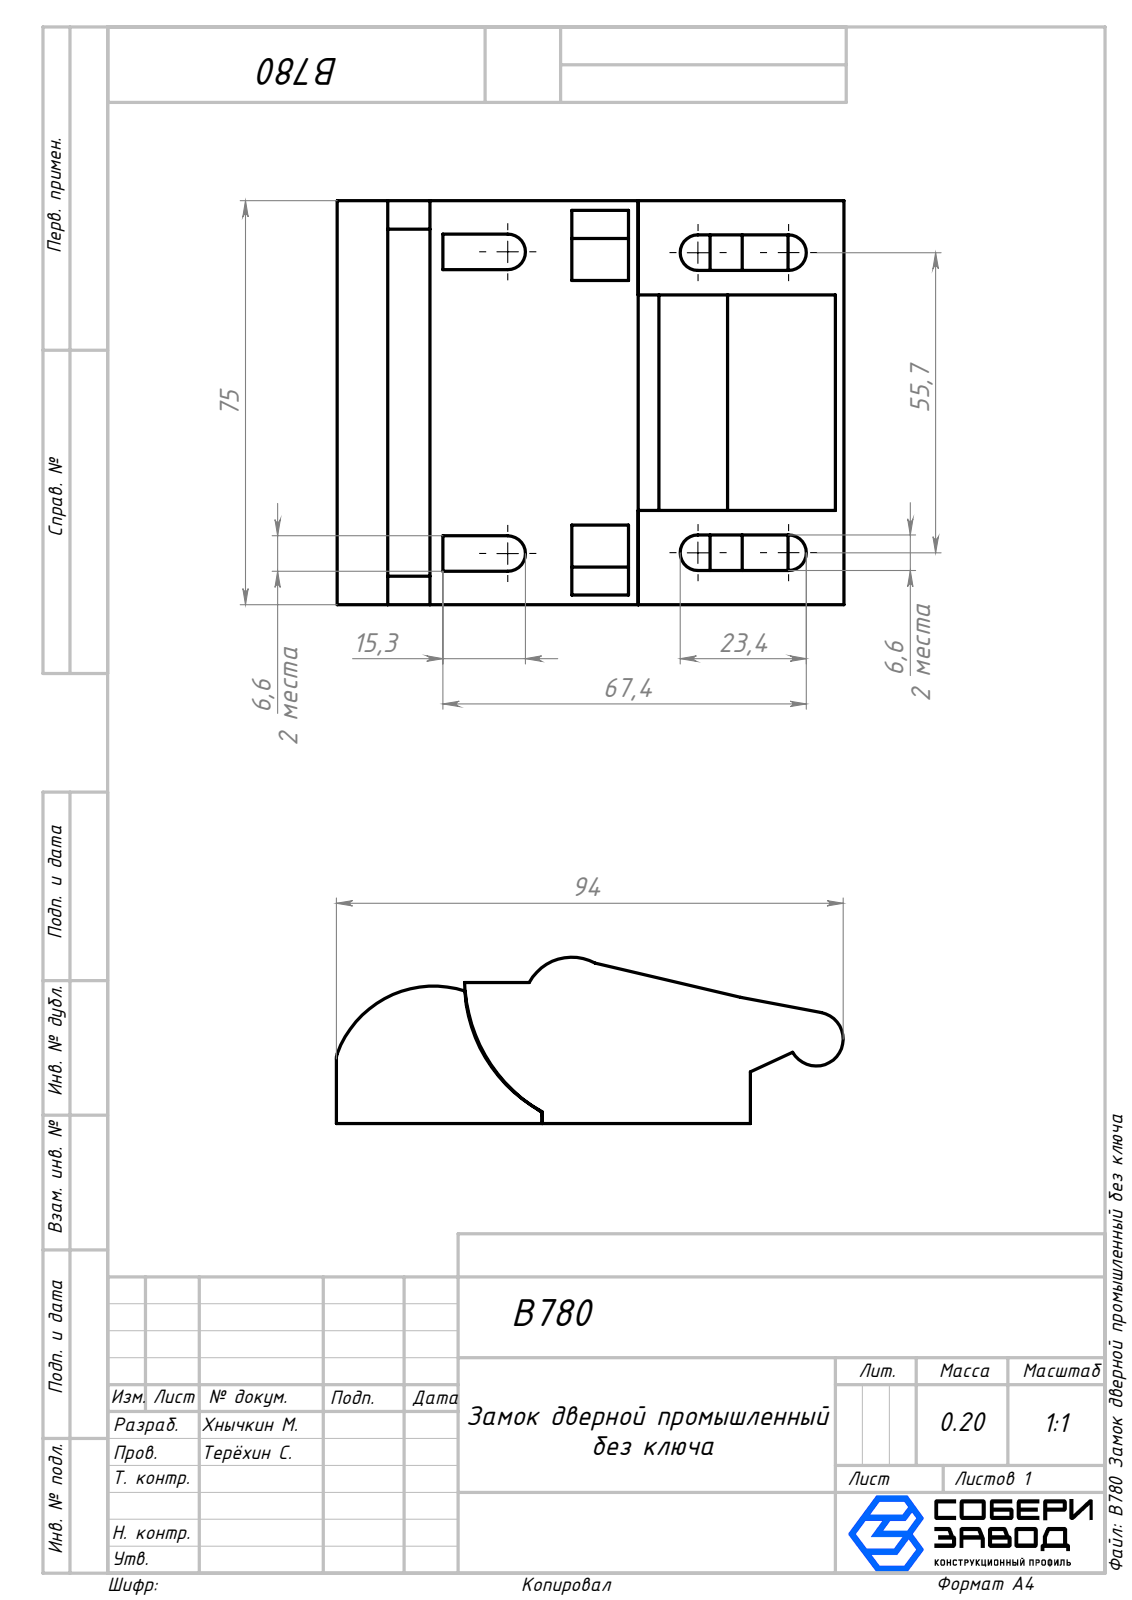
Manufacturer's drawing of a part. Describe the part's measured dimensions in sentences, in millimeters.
The part is named "Деталь2_00; Деталь1_00; B780 Замок дверной промышленный без ключа; Сборка для B780_00 (+1 more)". Its 3-D file was written by "SolidWorks 2025 (AUTOMOTIVE_DESIGN)". It is 4 solids with 135 faces: 96 planar, 39 cylindrical and 0 other. Overall it measures 94.03 by 75 by 30.9 millimeters. Its volume is 111 404 cubic millimeters and its surface area 37 439 square millimeters. Round holes: 2 of diameter 4. Partial cylindrical surfaces (rounded edges, fillets, slot ends): 6 of radius 3.3, 4 of radius 6.25, 3 of radius 28.65, 2 of radius 19, 1 of radius 1, 1 of radius 3, 1 of radius 5, 1 of radius 9. The main face-to-face distances are 75, 1.6, 14.1, 55.7, 17.5, 57.5, 38.6, 12.8, 3.4, 15.9. The hole center spacings are 55.7.
